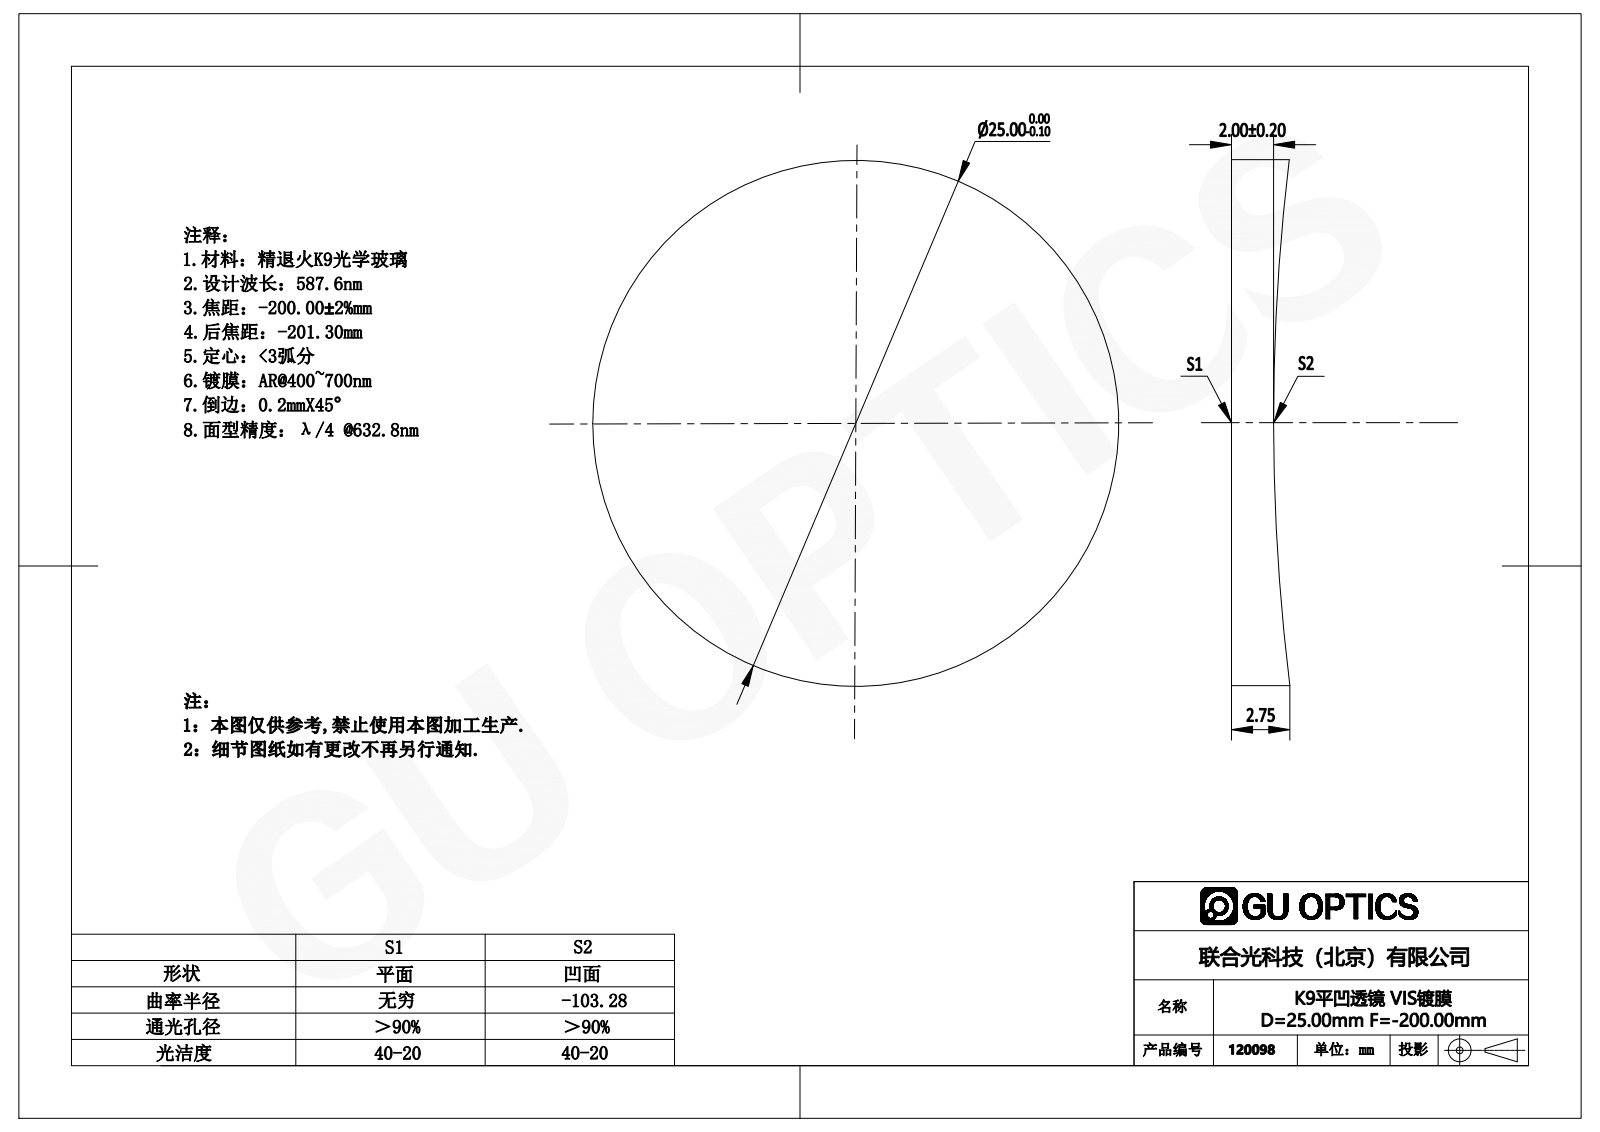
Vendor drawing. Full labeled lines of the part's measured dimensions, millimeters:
Part name (STEP PRODUCT): 120038
STEP written by: SolidWorks 2016 (AUTOMOTIVE_DESIGN)
Units: millimetres
Bodies: 1 solid, 5 faces (1 planar, 2 cylindrical, 2 other)
Overall size (bounding box): 25 × 25 × 2.75
Volume: 1 163 mm³ · Surface area: 1 199 mm²
Round bosses / shafts (diameter × count): ⌀25 ×1
